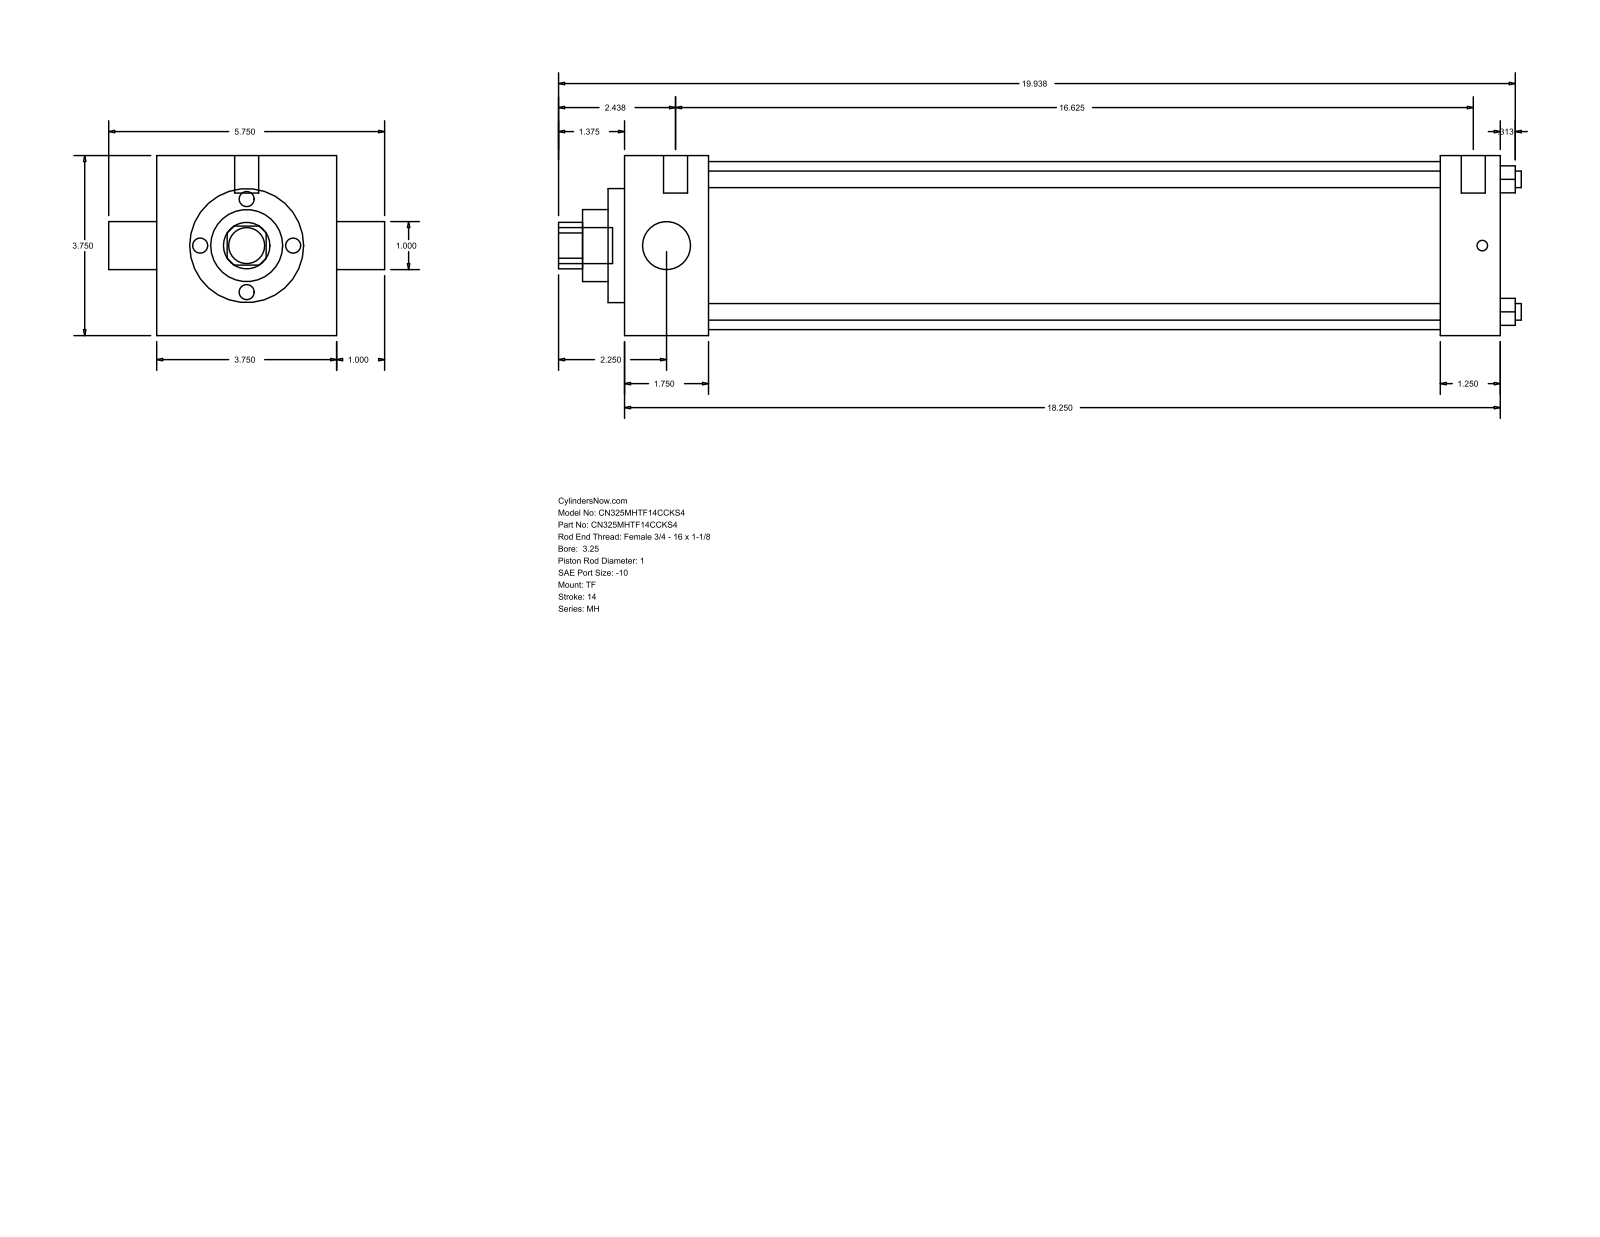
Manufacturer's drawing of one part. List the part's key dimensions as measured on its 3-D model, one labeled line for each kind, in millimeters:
Part name (STEP PRODUCT): MH_TF__0325_1
STEP written by: GSSL Pune (CONFIG_CONTROL_DESIGN)
Units: millimetres
Bodies: 0 solids, 86 faces (61 planar, 25 cylindrical, 0 other)
Overall size (bounding box): 509.59 × 146.05 × 95.25
Round holes (diameter × count): ⌀8.76 ×4, ⌀25.4 ×2, ⌀38.1 ×1, ⌀60.33 ×1, ⌀88.9 ×1
Round bosses / shafts (diameter × count): ⌀5.56 ×3, ⌀12.7 ×2, ⌀19.05 ×1
Partial cylindrical surfaces — rounded edges, fillets, slot ends (radius × count): R12.29 ×1
Main face-to-face distances: 95.24, 463.56, 44.46, 431.81, 387.35, 419.1, 31.75, 8.73, 53.19, 440.54
Hole centre spacings: 49.57, 70.1, 99.14
